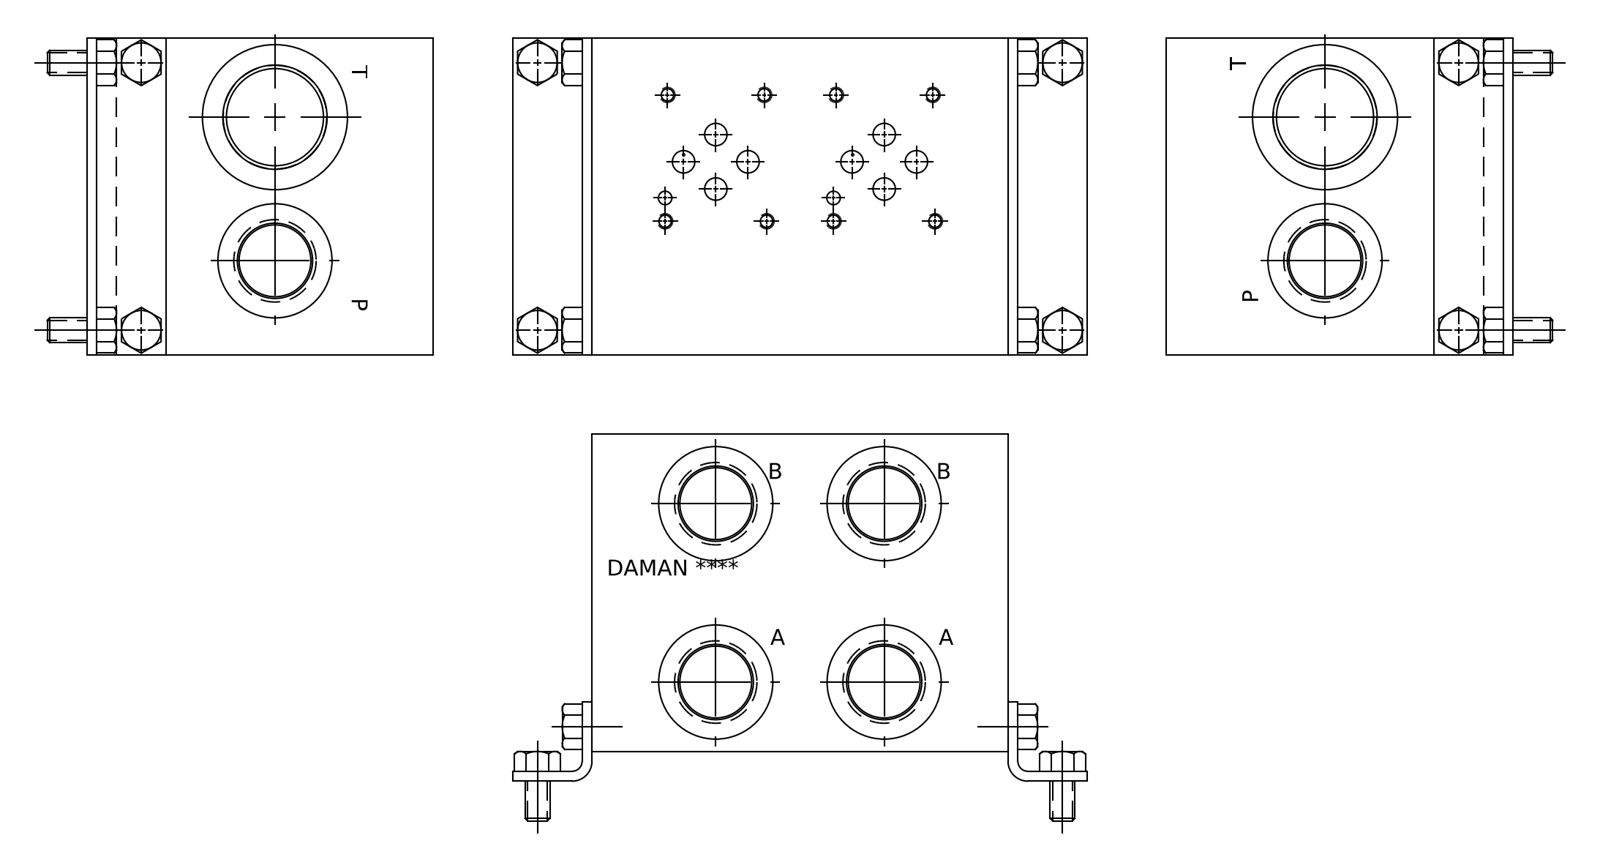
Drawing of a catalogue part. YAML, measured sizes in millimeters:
part_name: "Part_AD03HP022B_3D"
step_written_by: "Autodesk Inventor 2019 (AUTOMOTIVE_DESIGN)"
units: millimeters
bodies: {solids: 1, faces: 600, planar: 349, cylindrical: 66, other: 185}
overall_size: [133.35, 101.6, 101.6]
volume: 1217000
surface_area: 101026
round_holes:
  - {diameter: 4.22, count: 8}
  - {diameter: 5, count: 8}
  - {diameter: 6.35, count: 6}
  - {diameter: 24.41, count: 5}
  - {diameter: 26.54, count: 5}
  - {diameter: 37.11, count: 5}
  - {diameter: 23.01, count: 3}
  - {diameter: 3.96, count: 2}
  - {diameter: 6.76, count: 2}
  - {diameter: 7.14, count: 2}
  - {diameter: 8, count: 2}
  - {diameter: 10.72, count: 2}
face_to_face_distances: [101.6, 133.35, 0.79, 132.56, 100.81, 131.77, 17.88, 17.09, 83.72, 20.68]
hole_center_spacings: [53.98, 53.97, 22.04, 40.49, 51.45, 7.49, 13, 13.51]
